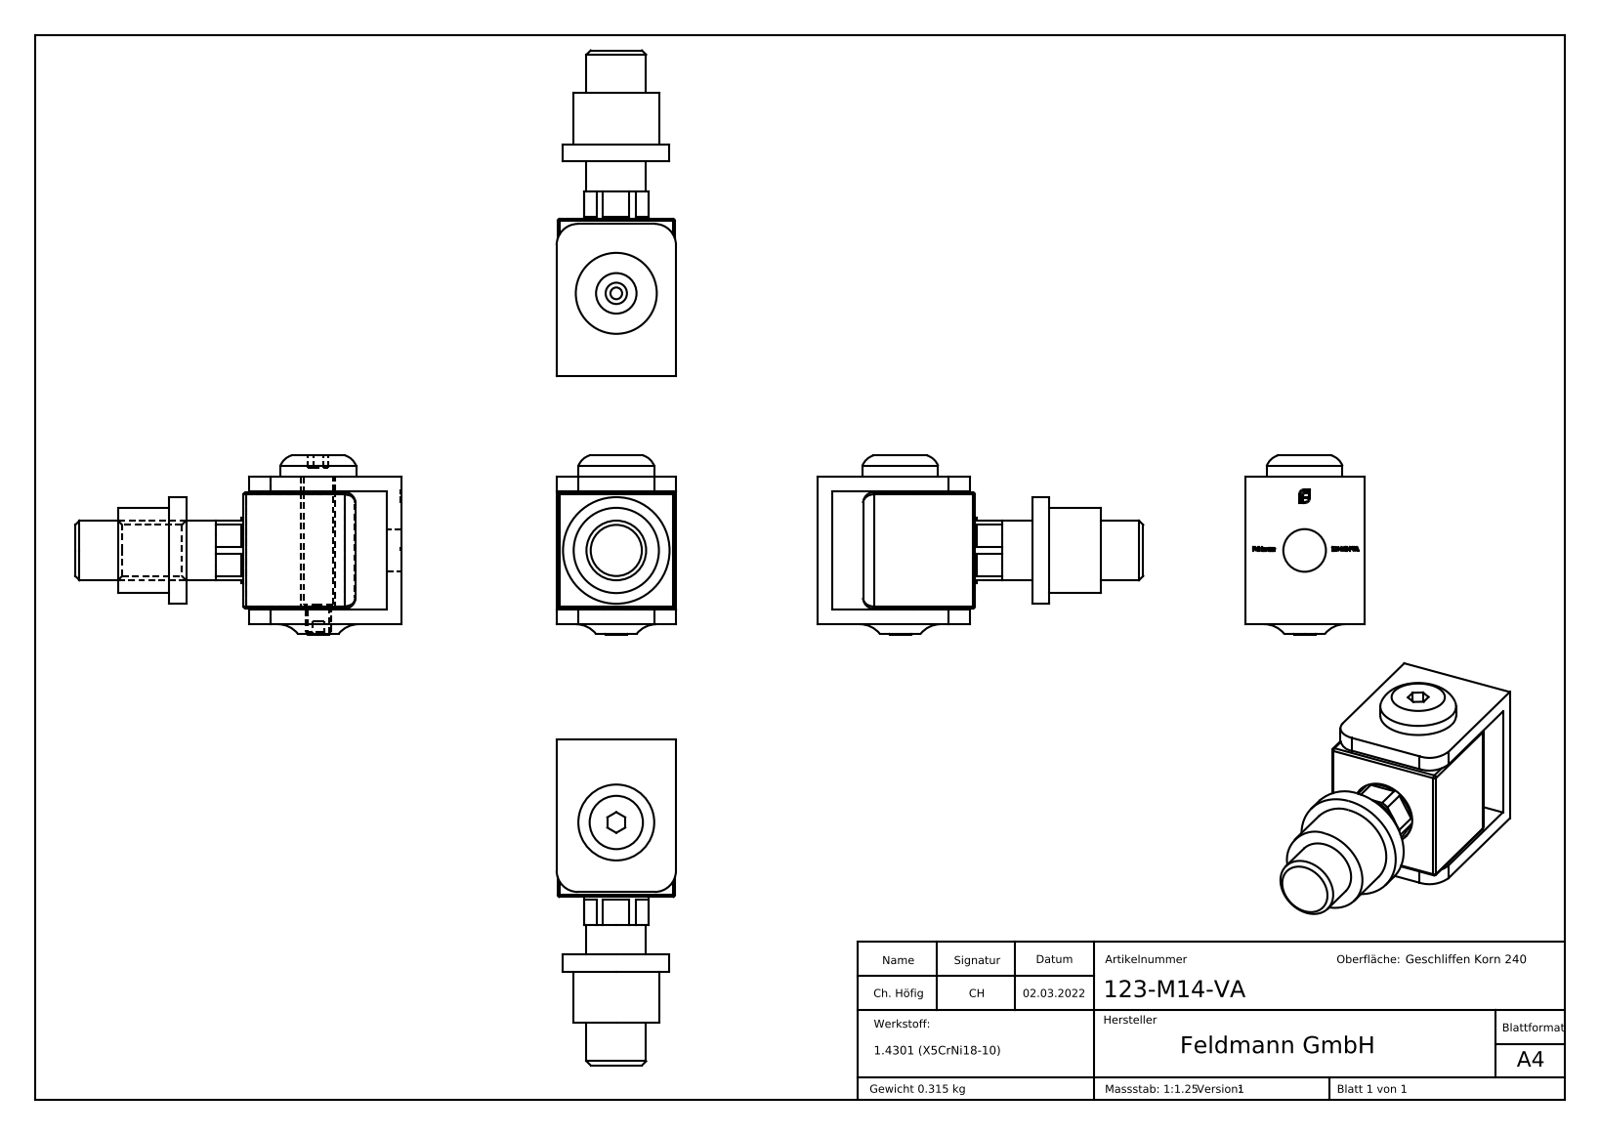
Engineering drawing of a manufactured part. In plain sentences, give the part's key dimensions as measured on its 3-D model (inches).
The part is named "123-MXX-VA Teil3_123-M14-VA Teil3; 123-M14-VA; 123-MXX-VA Teil1_123-M14-VA Teil1; 123-MXX-VA Teil2_123-M14-VA Teil2 (+1 more)". Its 3-D file was written by "SolidWorks 2018 (CONFIG_CONTROL_DESIGN)". It is 4 solids with 359 faces: 226 planar, 29 cylindrical and 104 other. Overall it measures 3.012 by 1.654 by 1.102 inches. Its volume is 2.435 cubic inches and its surface area 26.11 square inches. Round holes: 1 of diameter 0.108, 1 of diameter 0.197, 1 of diameter 0.315, 1 of diameter 0.319, 1 of diameter 0.394, 1 of diameter 0.472. Round bosses or shafts: 1 of diameter 0.984, 1 of diameter 0.787, 1 of diameter 0.701, 1 of diameter 0.602, 1 of diameter 0.551, 1 of diameter 0.268, 1 of diameter 0.236. Partial cylindrical surfaces (rounded edges, fillets, slot ends): 8 of radius 0.02, 4 of radius 0.098, 2 of radius 0.197. The main face-to-face distances are 0.138, 1.224, 0.144, 1.219, 1.081, 1.087, 1.362, 1.093, 1.083, 1.075.
